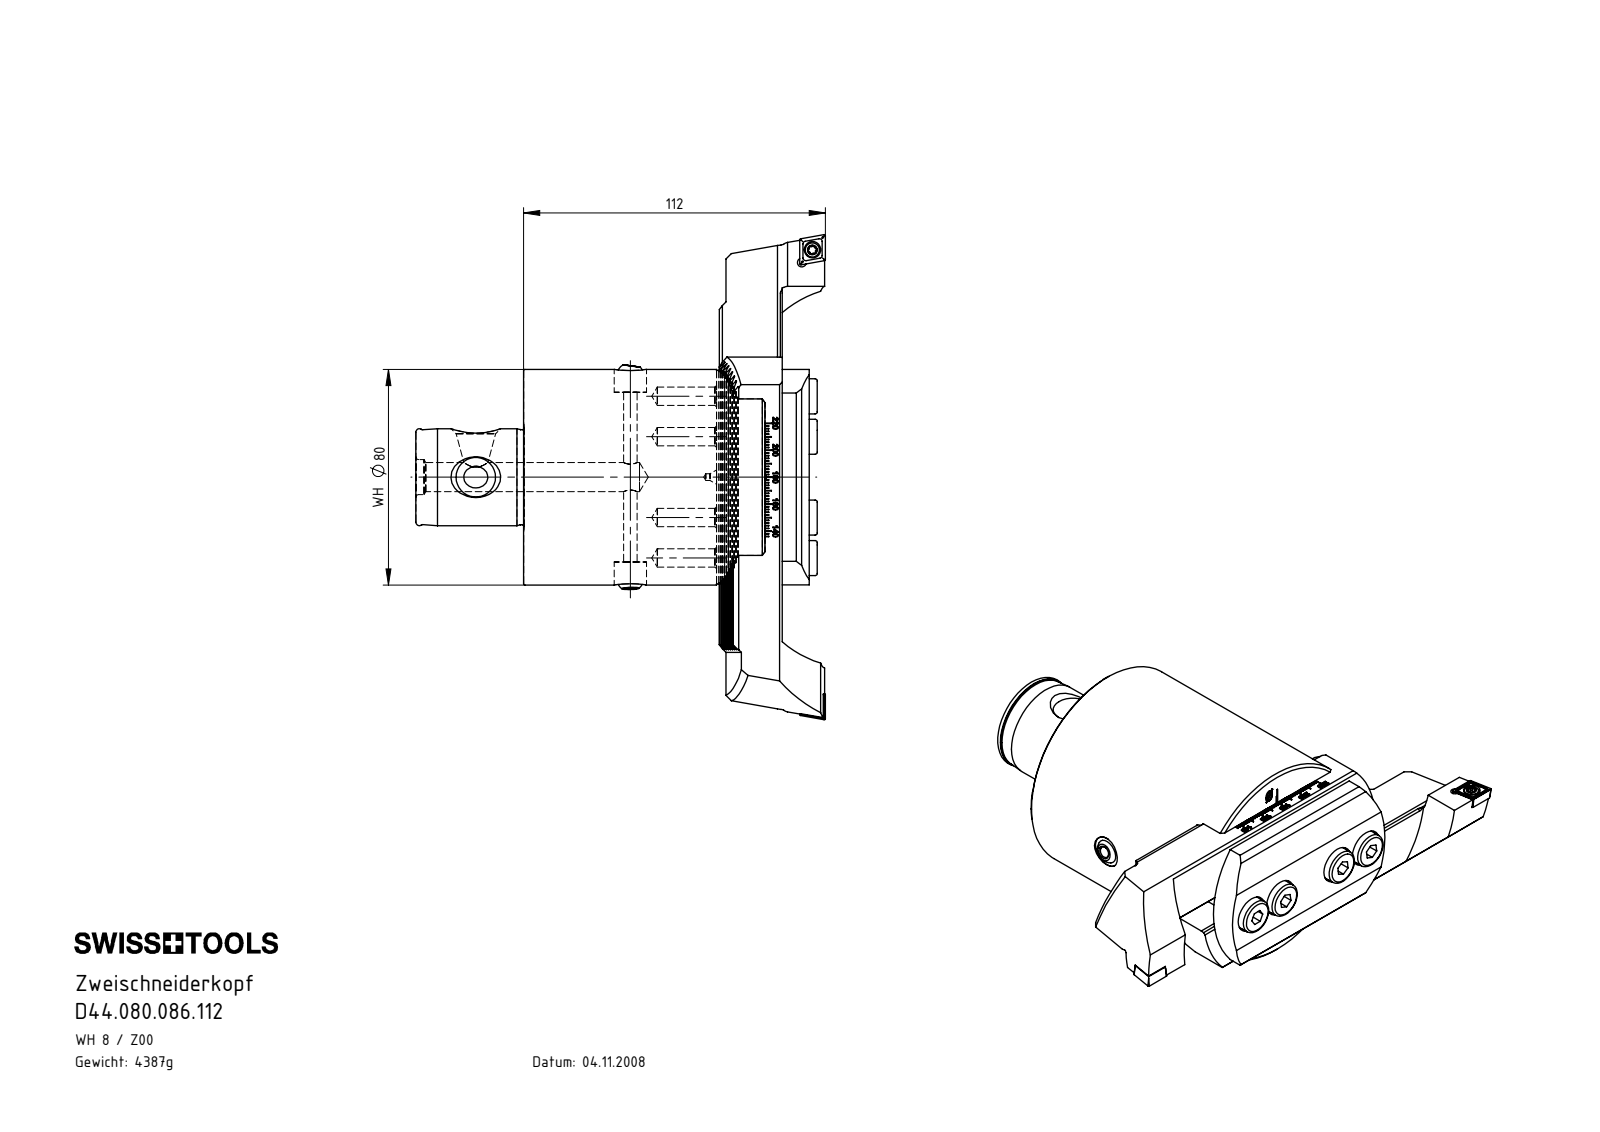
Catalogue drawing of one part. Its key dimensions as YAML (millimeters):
part_name: "F00-WCB.136.002_A; KU1-U12.001.010; F00-WCB.136.001; CCMT09T304 (+7 more)"
step_written_by: "SolidWorks 2017 (CONFIG_CONTROL_DESIGN)"
units: millimeters
bodies: {solids: 16, faces: 1520, planar: 863, cylindrical: 168, other: 489}
overall_size: [180.01, 152.03, 80]
volume: 568556
surface_area: 92418
round_holes:
  - {diameter: 6.8, count: 5}
  - {diameter: 3.3, count: 4}
  - {diameter: 8.5, count: 4}
  - {diameter: 14, count: 4}
  - {diameter: 4.4, count: 2}
  - {diameter: 6.1, count: 2}
  - {diameter: 2.5, count: 1}
  - {diameter: 4.2, count: 1}
  - {diameter: 7, count: 1}
  - {diameter: 10.8, count: 1}
  - {diameter: 12, count: 1}
  - {diameter: 13, count: 1}
round_bosses_or_shafts:
  - {diameter: 13, count: 4}
  - {diameter: 8, count: 4}
  - {diameter: 5.25, count: 2}
  - {diameter: 4, count: 2}
  - {diameter: 80, count: 1}
  - {diameter: 36, count: 1}
  - {diameter: 35.3, count: 1}
partial_cylinders:
  - {radius: 0.2, count: 32}
  - {radius: 0.34, count: 12}
  - {radius: 0.59, count: 12}
  - {radius: 40, count: 8}
  - {radius: 0.8, count: 2}
face_to_face_distances: [2.38, 4.76, 7.14, 21.3, 33.7, 96.03, 9.52, 12.4, 9.53, 14.29]
hole_center_spacings: [15, 30, 6.07, 6.2, 45, 164.02, 164.12, 168.72]
